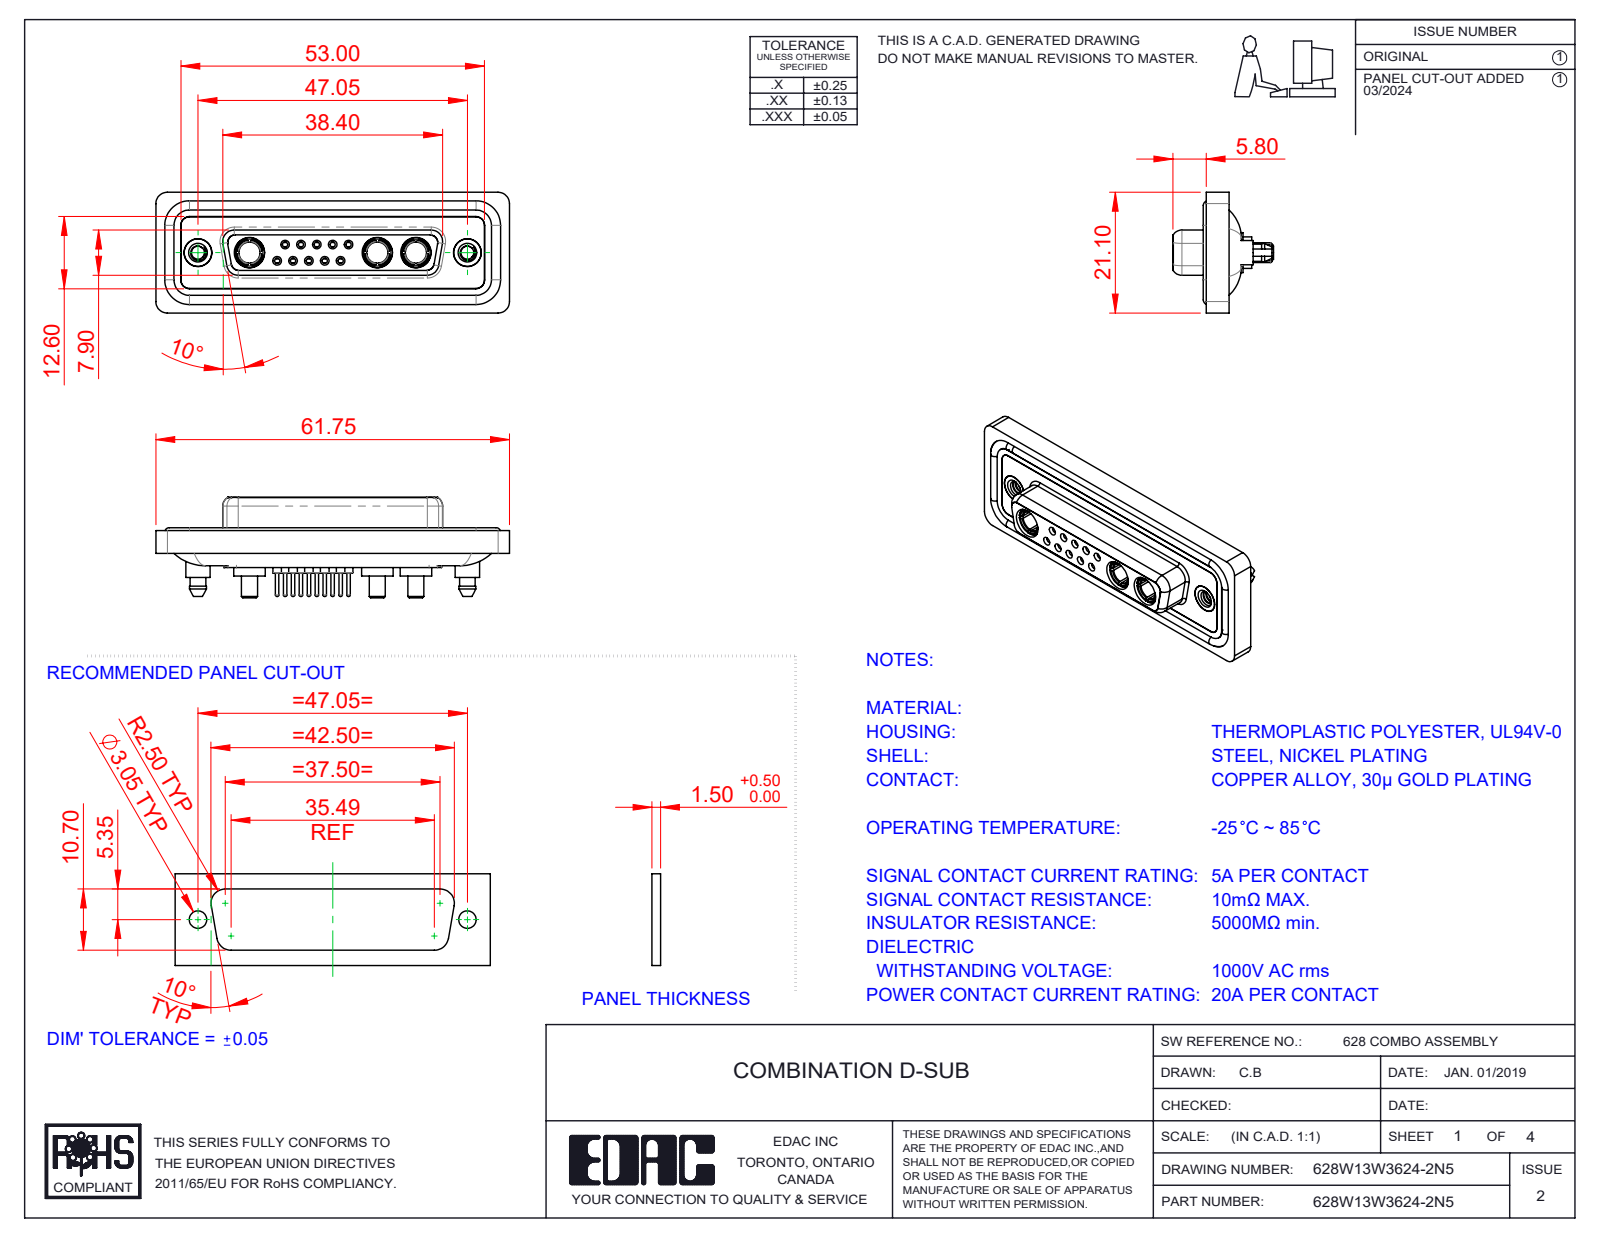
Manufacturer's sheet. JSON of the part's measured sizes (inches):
{"part_name": "Power Socket_20A S; 628Combo Shell Front_25 Contacts; 628Combo Waterproof Housing_25 Contacts; 628Combo Housing_13W3 (+5 more)", "step_written_by": "SolidWorks 2023 (CONFIG_CONTROL_DESIGN)", "units": "inches", "bodies": {"solids": 23, "faces": 1208, "planar": 358, "cylindrical": 479, "other": 371}, "overall_size": [2.431, 0.831, 0.691], "volume_in3": 0.513, "surface_area_in2": 21.77, "round_holes": [[0.035, 10], [0.043, 10], [0.059, 10], [0.079, 10], [0.063, 5], [0.067, 5], [0.191, 5], [0.146, 3], [0.209, 3], [0.089, 2], [0.157, 2], [0.159, 2]], "round_bosses_or_shafts": [[0.087, 10], [0.024, 10], [0.063, 9], [0.217, 3], [0.205, 3], [0.195, 3], [0.187, 3], [0.148, 3]], "partial_cylinders_radius": [[0.059, 24], [0.079, 18], [0.063, 10], [0.053, 8], [0.01, 4], [0.02, 4], [0.024, 4], [0.026, 4]], "face_to_face_distances": [0.016, 0.071, 0.293, 0.222, 0.02, 0.26, 0.278, 0.063, 0.114, 0.043], "hole_center_spacings": [0.124, 0.109, 0.198, 0.198, 0.218, 0.327, 0.295, 0.109]}
